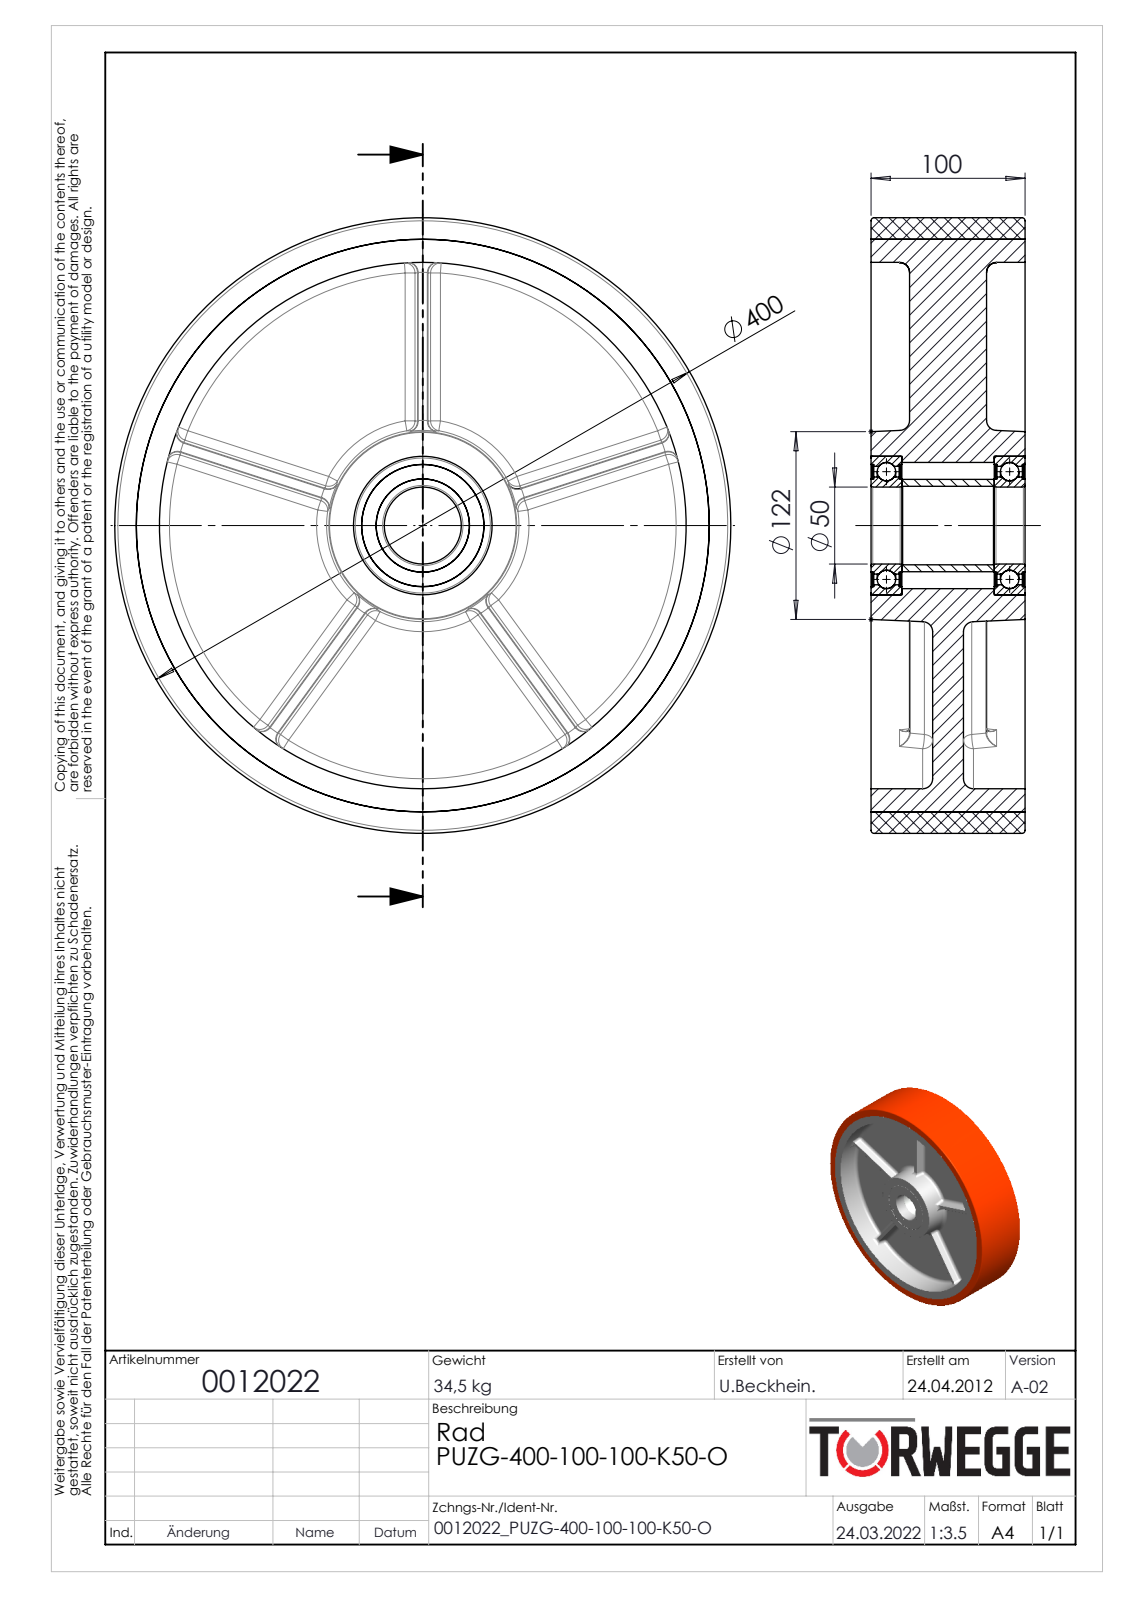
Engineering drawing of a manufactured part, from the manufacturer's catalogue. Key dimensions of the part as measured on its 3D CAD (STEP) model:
Part name (STEP PRODUCT): 0012022
STEP written by: SolidWorks 2020 (AUTOMOTIVE_DESIGN)
Units: millimetres
Bodies: 13 solids, 454 faces (74 planar, 116 cylindrical, 264 other)
Overall size (bounding box): 400 × 400 × 100
Volume: 6 000 000 mm³ · Surface area: 855 649 mm²
Round holes (diameter × count): ⌀50 ×1, ⌀51 ×1, ⌀60.6 ×1, ⌀76.96 ×1, ⌀79.4 ×1, ⌀82 ×1, ⌀90 ×1, ⌀342 ×1, ⌀372 ×1
Round bosses / shafts (diameter × count): ⌀400 ×1, ⌀63.04 ×1, ⌀60 ×1
Partial cylindrical surfaces — rounded edges, fillets, slot ends (radius × count): R0.5 ×20, R6.5 ×20
Main face-to-face distances: 40, 60, 20, 100, 80, 0.88, 15.3, 19.12, 18.24, 25
